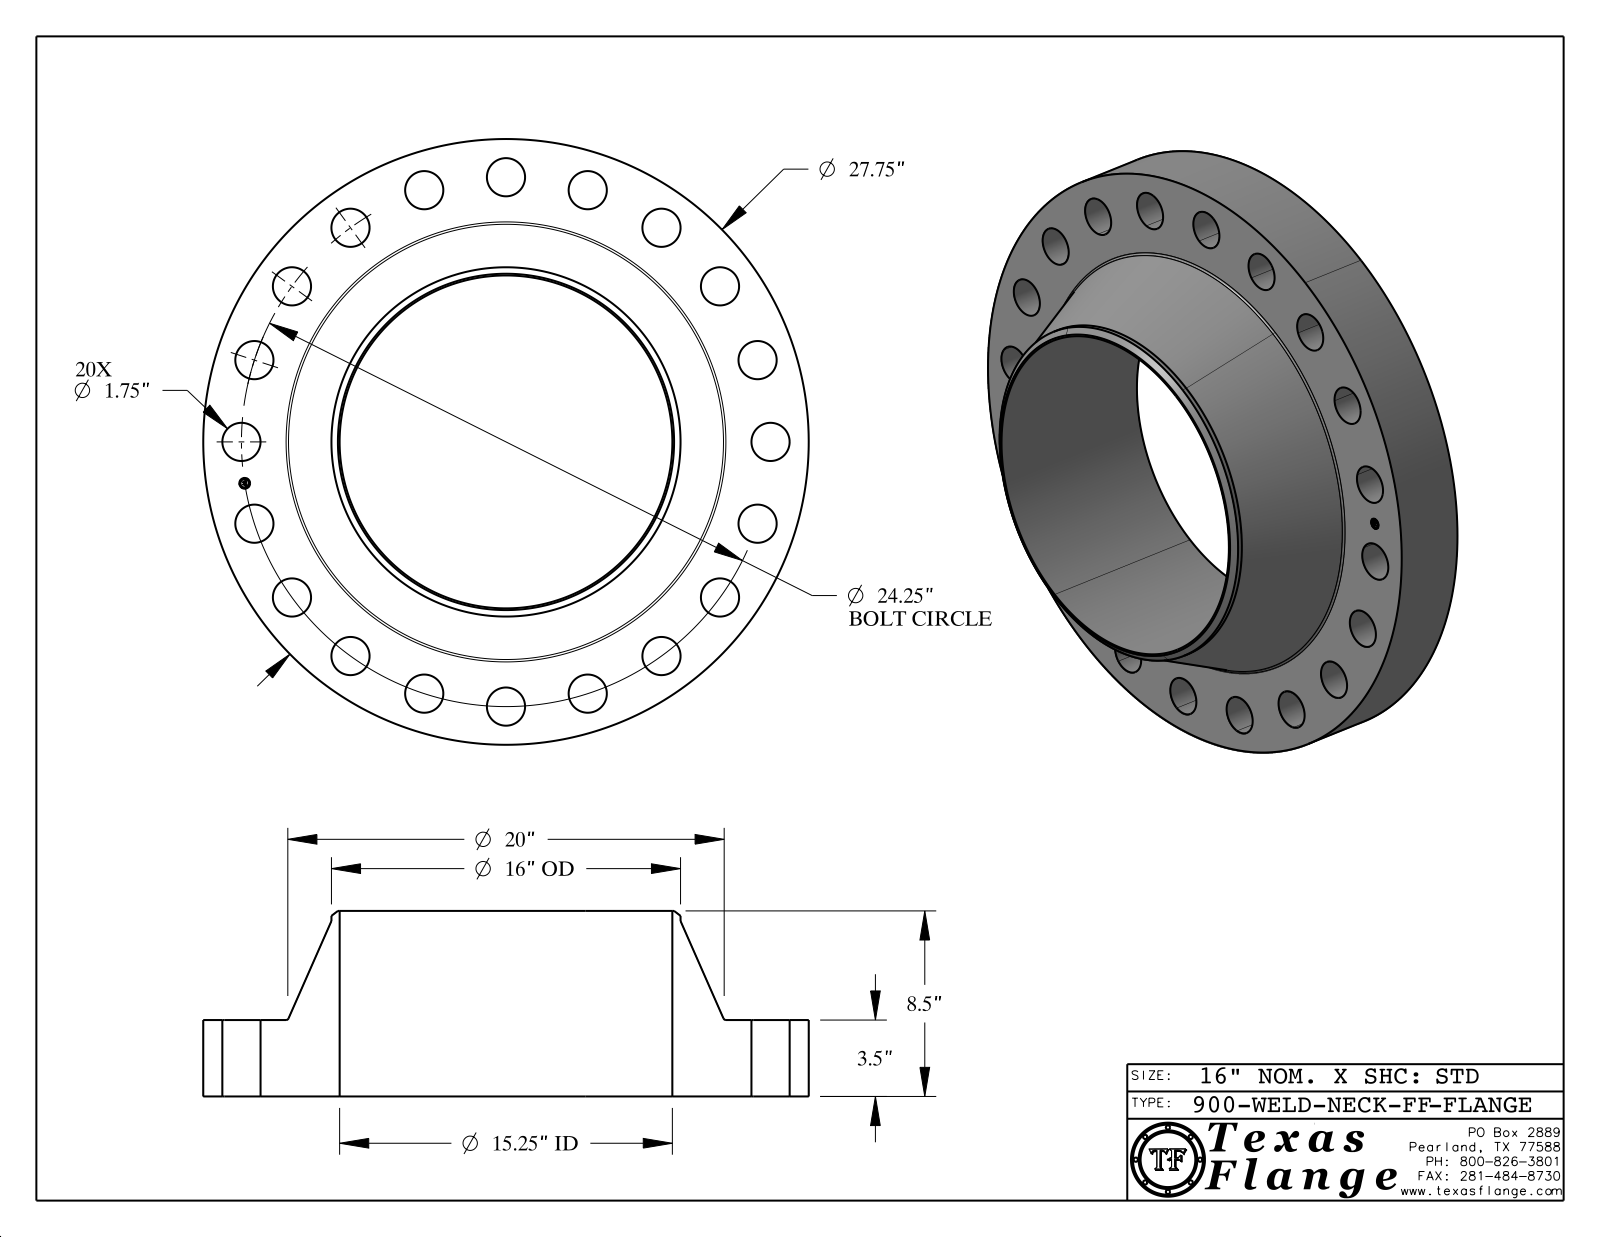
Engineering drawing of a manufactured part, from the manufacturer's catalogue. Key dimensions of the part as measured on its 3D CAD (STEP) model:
Part name (STEP PRODUCT): 900-WELD-NECK-FF
STEP written by: CATIA V5 STEP AP214 (AUTOMOTIVE_DESIGN)
Units: inches
Bodies: 1 solid, 440 faces (368 planar, 66 cylindrical, 6 other)
Overall size (bounding box): 27.75 × 27.75 × 8.5
Volume: 1 647 in³ · Surface area: 2 027 in²
Round holes (diameter × count): ⌀1.75 ×20, ⌀0.495 ×1, ⌀15.25 ×1
Round bosses / shafts (diameter × count): ⌀0.03 ×8, ⌀27.75 ×1, ⌀16 ×1, ⌀0.39 ×1
Main face-to-face distances: 3.5, 8.5, 5, 3.485, 0.015, 5.015, 0.148, 0.145, 0.027, 0.096
Hole centre spacings: 17.147, 23.063, 19.619, 12.125, 3.794, 7.494, 11.009, 14.254
